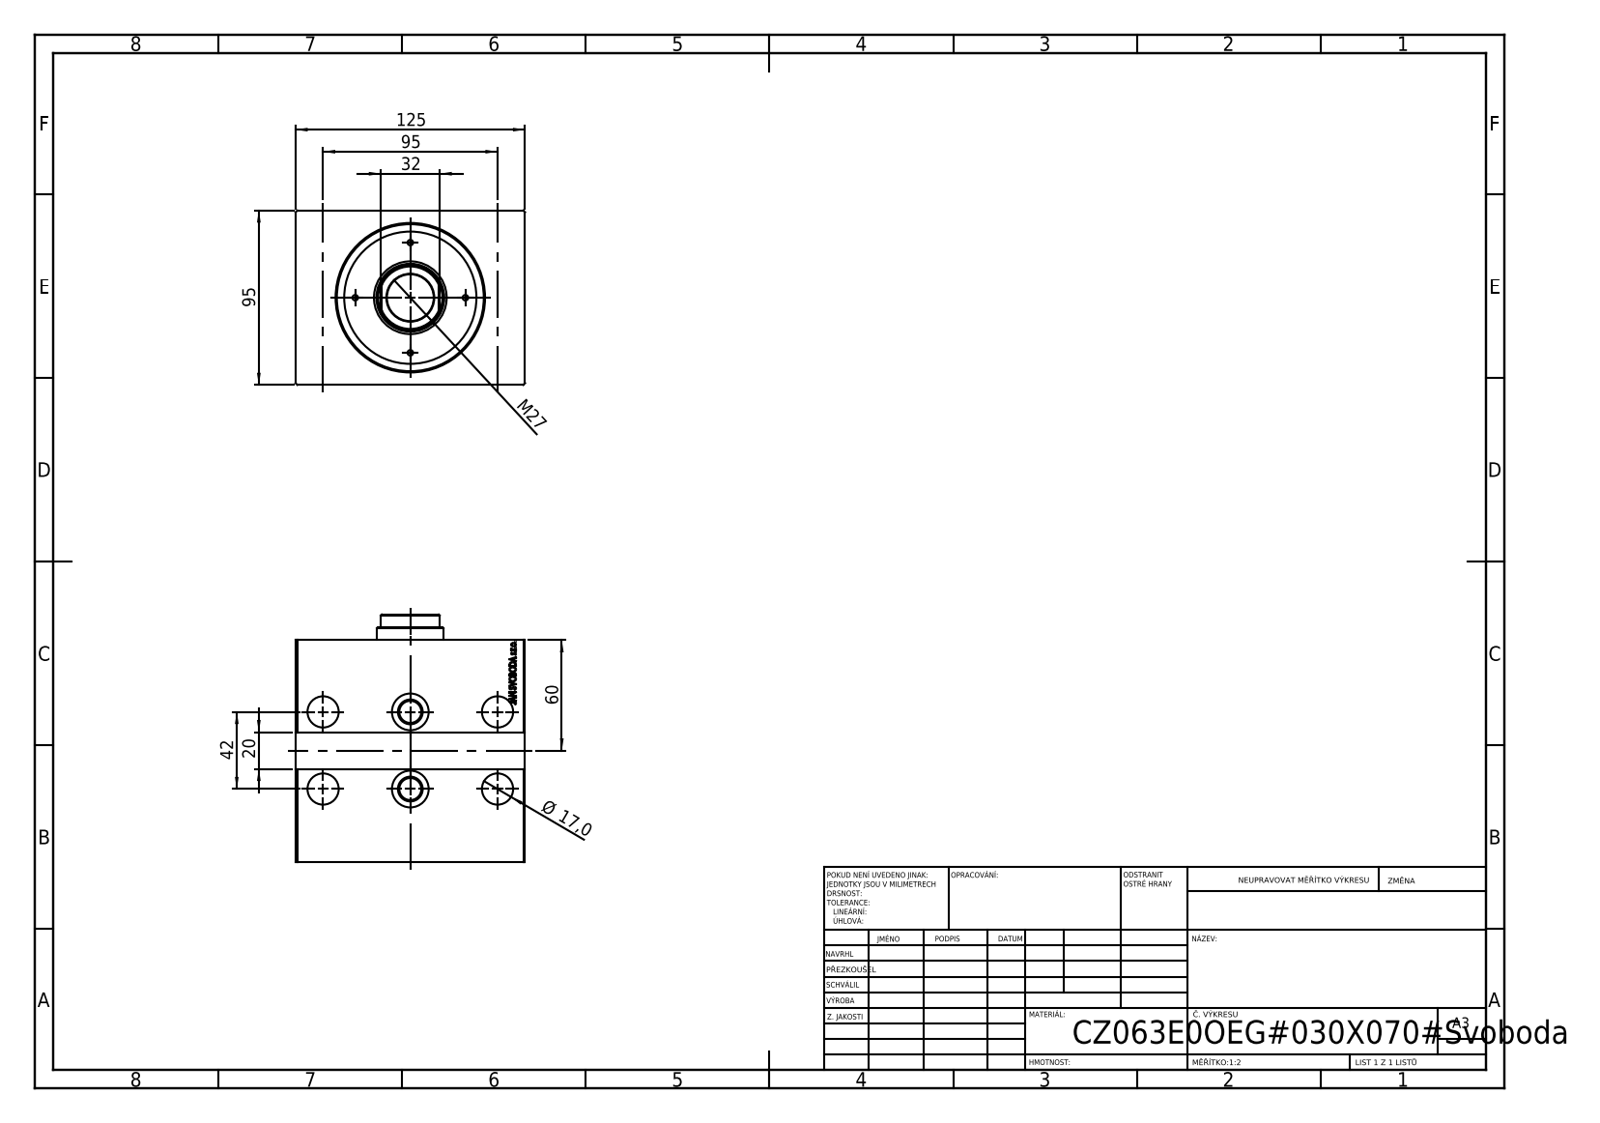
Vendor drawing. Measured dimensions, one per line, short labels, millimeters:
written by: SolidWorks 2019 (CONFIG_CONTROL_DESIGN)
unit: mm
bodies: 1 solid, 805 faces (393 planar, 30 cylindrical, 382 other)
size: 125 × 121 × 95
volume: 1 004 000 mm³; area: 116 955 mm²
holes: 4× ⌀17, 2× ⌀8, 2× ⌀12, 2× ⌀20, 1× ⌀36, 1× ⌀63, 1× ⌀80
bosses: 2× ⌀13.5
face distances: 125, 95, 121, 100.2, 20.8, 2, 93, 14, 86.2, 107
hole spacings: 47.5, 63.41, 42, 95, 103.87, 20.52, 22.81, 27.02
